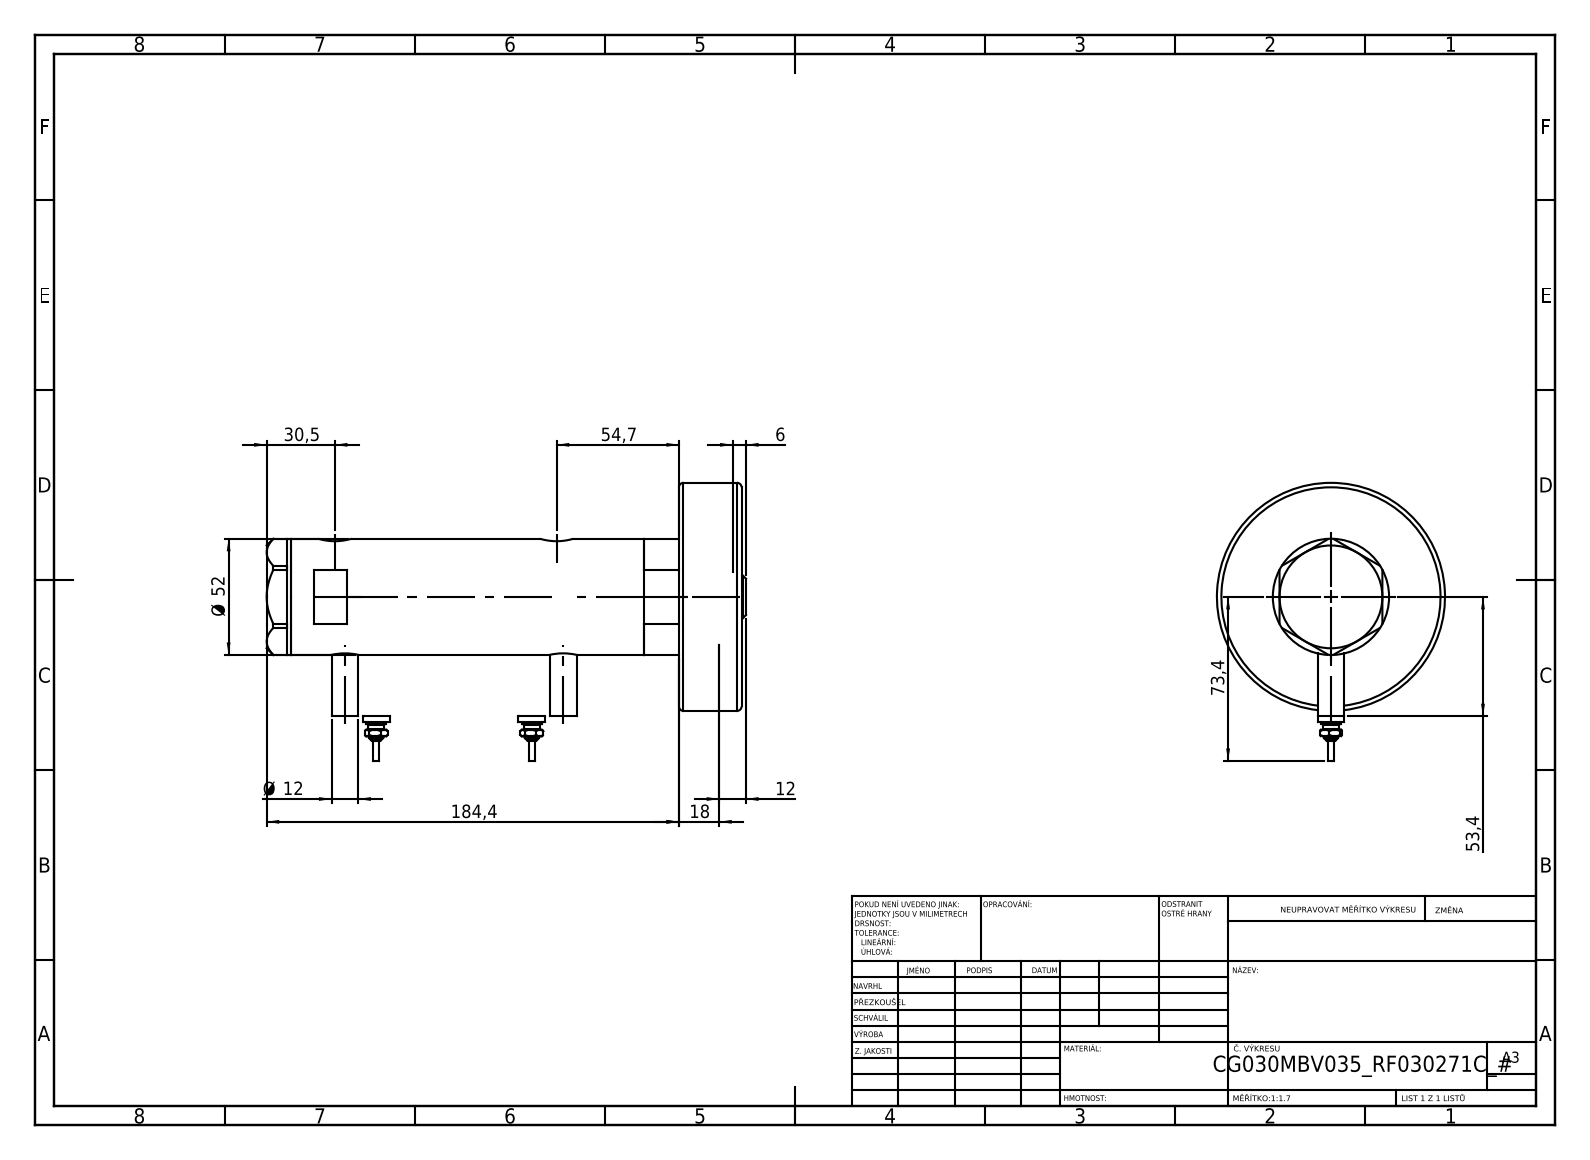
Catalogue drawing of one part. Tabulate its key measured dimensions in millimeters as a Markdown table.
| quantity | value |
| --- | --- |
| part name | V270CG_271C; V270CG_FRONT; V270CG_VC; V270CG_BACK (+2 more) |
| STEP written by | SolidWorks 2019 (CONFIG_CONTROL_DESIGN) |
| units | millimeters |
| bodies | 7 solids, 236 faces (95 planar, 73 cylindrical, 68 other) |
| overall size | 214.4 × 124.4 × 102 |
| volume | 595 747 mm³ |
| surface area | 116 078 mm² |
| round holes (diameter × count) | 9.73 × 2, 12.5 × 2, 15 × 2, 6.5 × 1, 20 × 1, 21.5 × 1, 30 × 1, 33 × 1, 40 × 1, 44 × 1 |
| round bosses / shafts (diameter × count) | 12 × 4, 9 × 2, 7 × 2, 4.5 × 2, 2.5 × 2, 102 × 1, 52 × 1, 38 × 1 |
| main face-to-face distances | 28, 173.4, 201.4, 121.5, 51.9, 79.9, 23.8, 97.7, 149.6, 177.6 |
| hole center spacings | 2.9, 4.5, 94.7, 97.6, 99.2, 102.1 |
